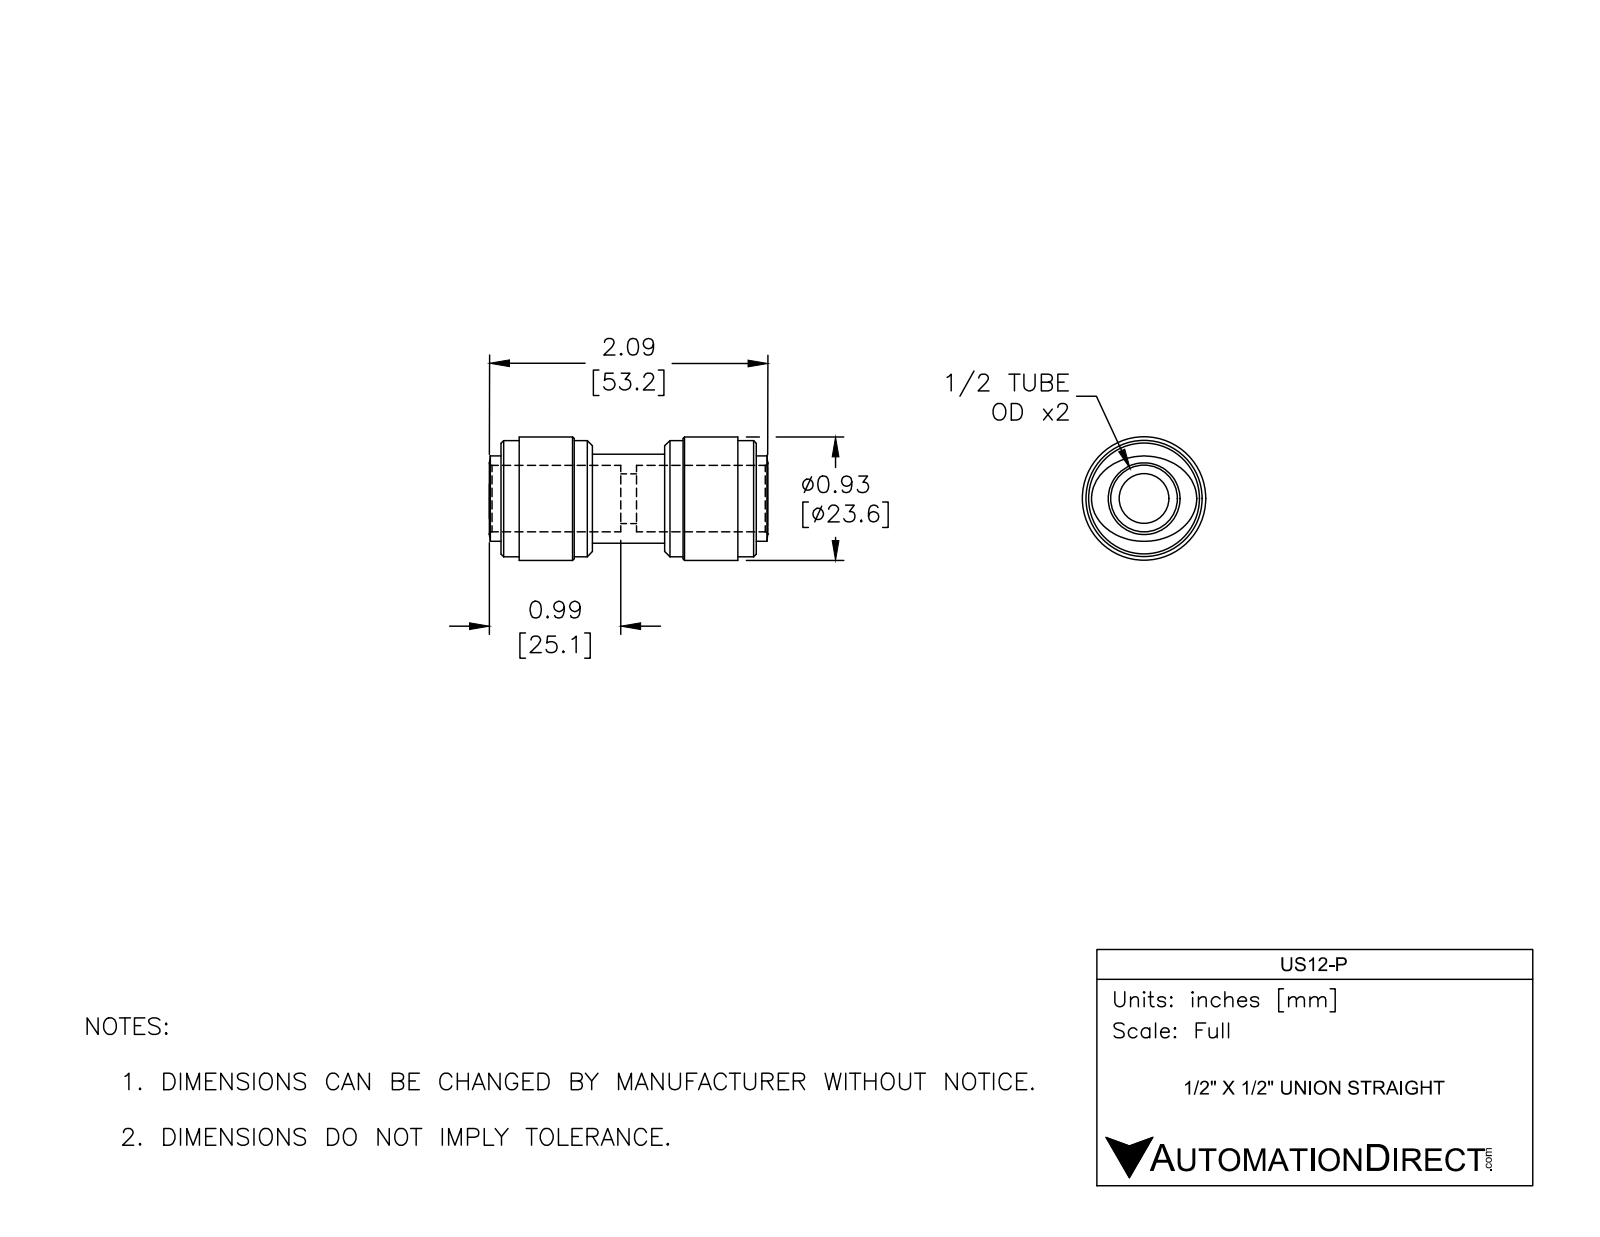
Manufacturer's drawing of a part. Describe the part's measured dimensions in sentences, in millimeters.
The part is named "US12-P". Its 3-D file was written by "SolidWorks 2017 (AUTOMOTIVE_DESIGN)". It is 1 solid with 54 faces: 10 planar, 20 cylindrical and 24 other. Overall it measures 53.2 by 23.6 by 23.6 millimeters. Its volume is 12 200 cubic millimeters and its surface area 6 581 square millimeters. Round holes: 1 of diameter 9.5, 1 of diameter 12.7. Round bosses or shafts: 1 of diameter 23.6, 1 of diameter 22.2, 1 of diameter 17. The main face-to-face distances are 31.3, 17.5, 3.5, 14, 22.9, 25.9, 5.4, 8.4, 45.3, 19.4.
